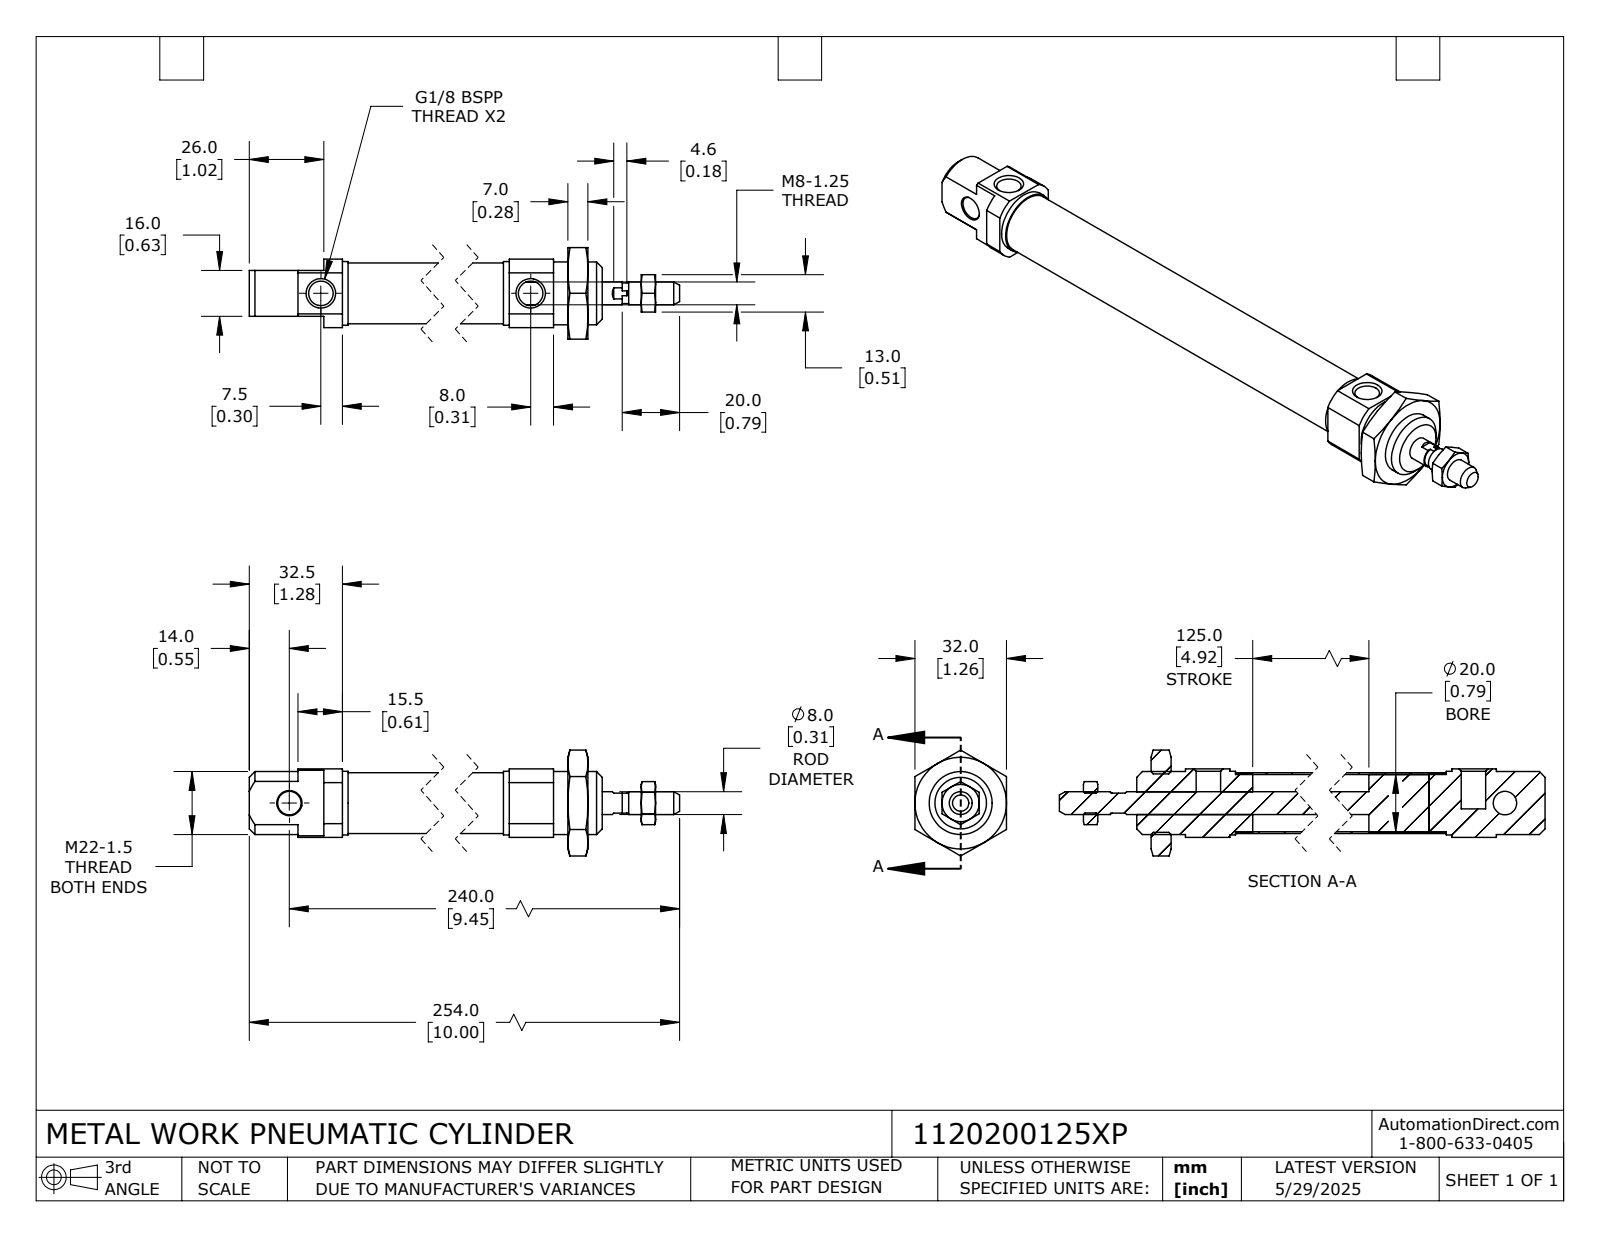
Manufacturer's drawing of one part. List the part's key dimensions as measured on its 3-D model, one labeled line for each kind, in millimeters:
Part name (STEP PRODUCT): 1120200125XP_BODY; 1120200125XP; 1120200125XP_ROD
STEP written by: SolidWorks 2024 (CONFIG_CONTROL_DESIGN)
Units: millimetres
Bodies: 6 solids, 147 faces (56 planar, 45 cylindrical, 46 other)
Overall size (bounding box): 254 × 36.95 × 32
Volume: 55 134 mm³ · Surface area: 39 710 mm²
Round holes (diameter × count): ⌀8.57 ×2, ⌀6.92 ×1, ⌀8.2 ×1, ⌀20 ×1, ⌀20.38 ×1
Round bosses / shafts (diameter × count): ⌀22.2 ×1, ⌀22 ×1, ⌀21.27 ×1, ⌀20.15 ×1, ⌀8 ×1, ⌀7.2 ×1
Partial cylindrical surfaces — rounded edges, fillets, slot ends (radius × count): R13.95 ×1
Main face-to-face distances: 3.97, 19.97, 23.94, 8, 40.5, 186.5, 7, 5, 181.5, 174.5
Hole centre spacings: 177
